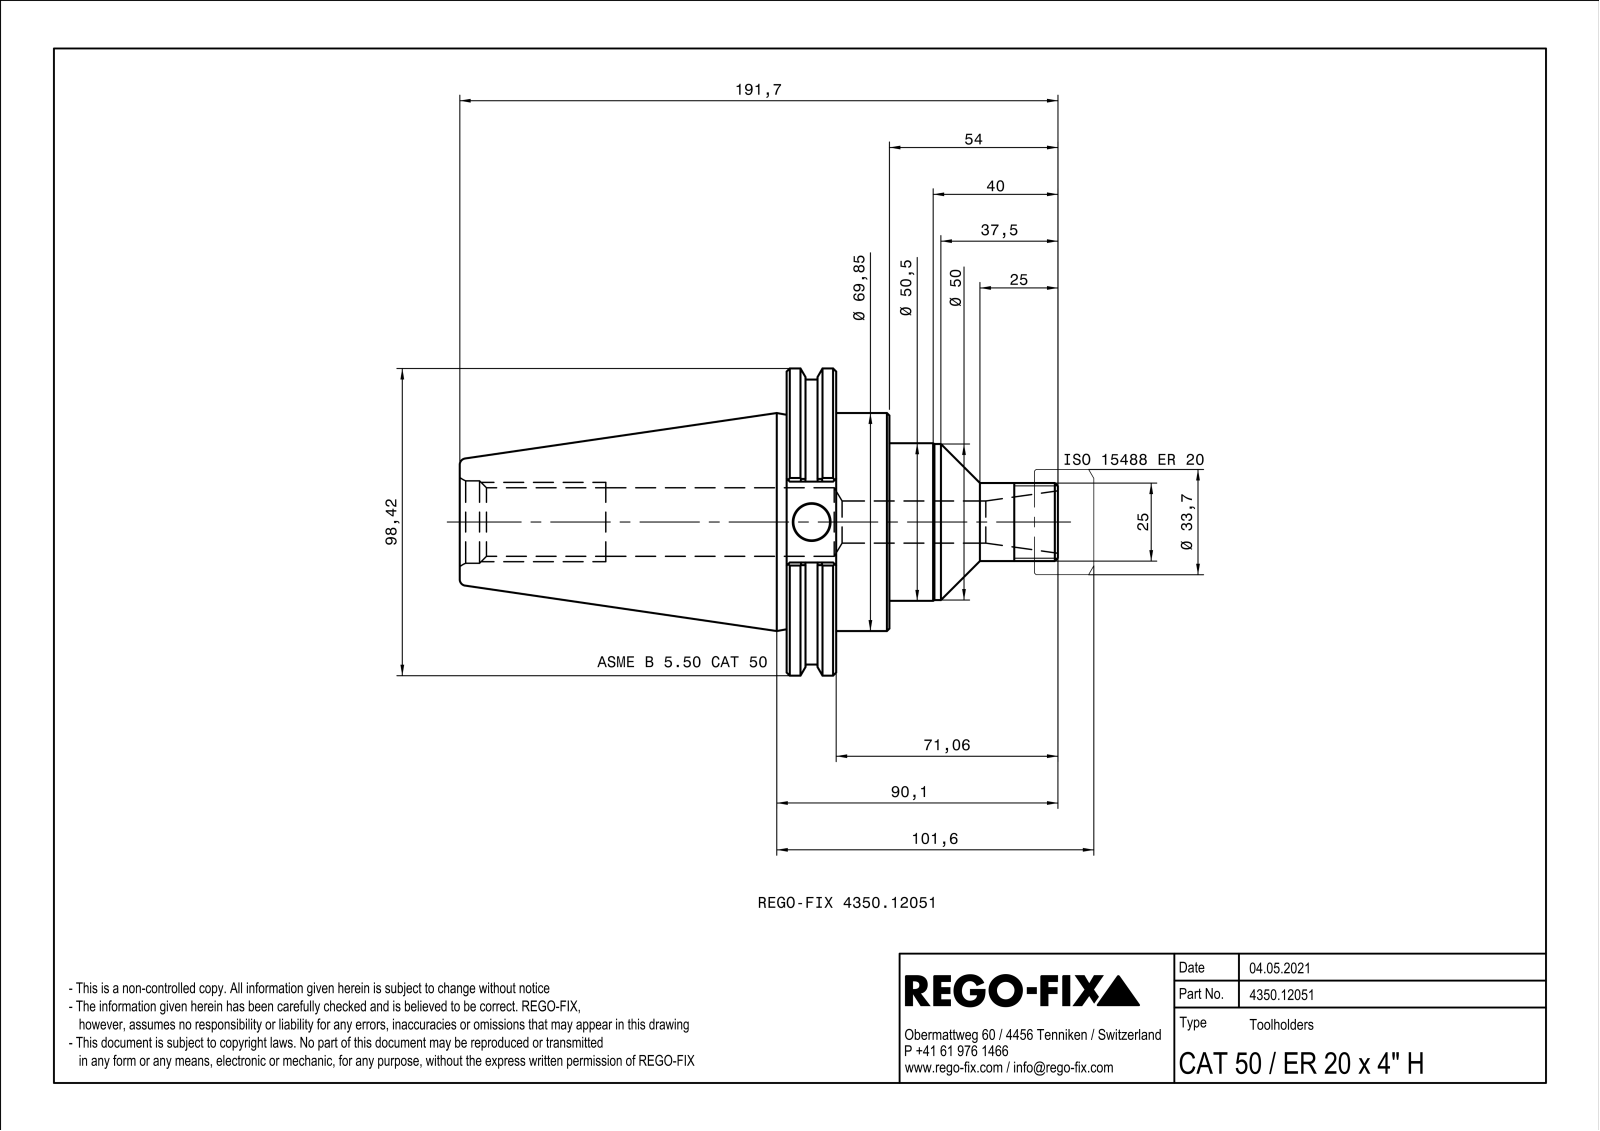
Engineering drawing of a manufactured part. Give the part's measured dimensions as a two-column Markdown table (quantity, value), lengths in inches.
| quantity | value |
| --- | --- |
| part name | NOCUT |
| STEP written by | SIEMENS PLM Software Solid Edge ST10 (AUTOMOTIVE_DESIGN) |
| units | inches |
| bodies | 1 solid, 109 faces (31 planar, 31 cylindrical, 47 other) |
| overall size | 7.547 × 3.875 × 3.716 |
| volume | 26.2 in³ |
| surface area | 86.94 in² |
| round holes (diameter × count) | 0.461 × 1, 0.531 × 1, 0.865 × 1, 0.865 × 1, 1.039 × 1 |
| round bosses / shafts (diameter × count) | 3.875 × 1, 3.594 × 1, 2.75 × 1, 1.988 × 1, 1.969 × 1, 0.984 × 1 |
| partial cylindrical surfaces (radius × count) | 0.02 × 12 |
| main face-to-face distances | 0.625, 0.672, 1.296, 5.421, 4.75, 4.125, 2.863, 1.02, 0.907, 0.236 |
